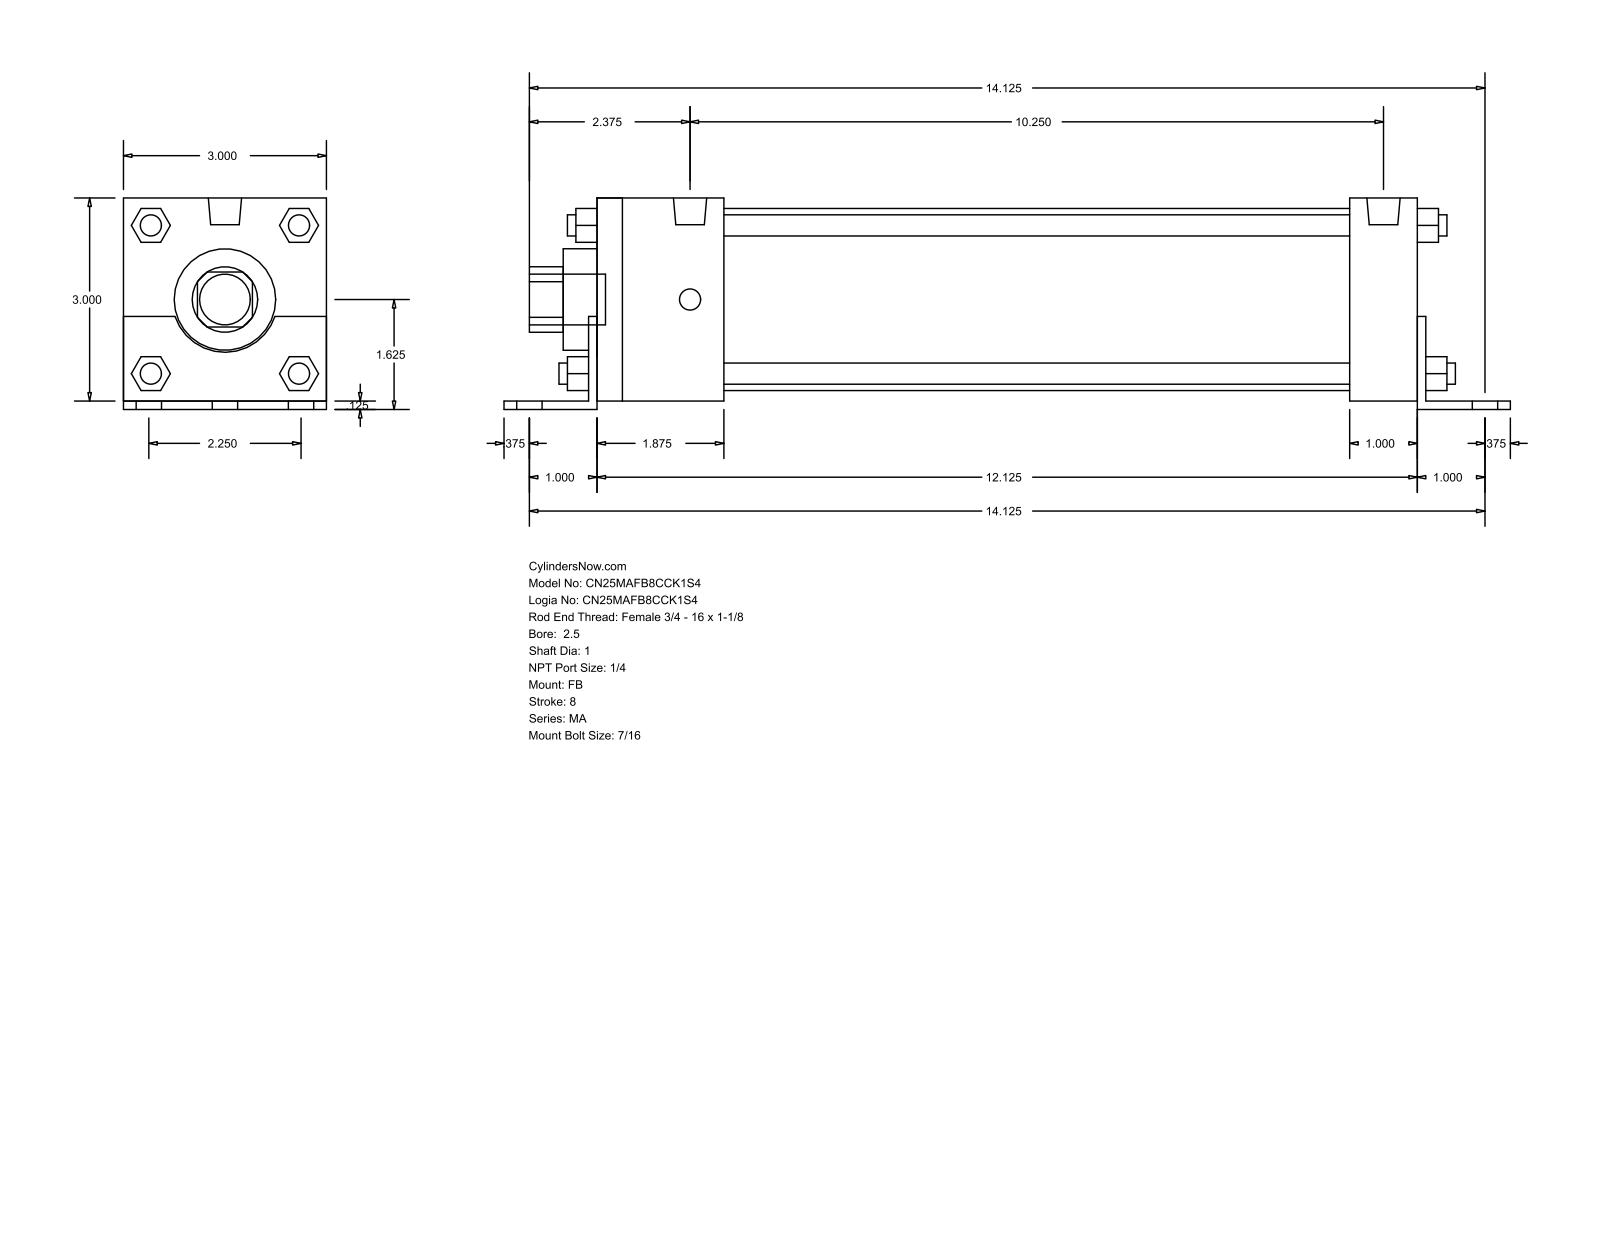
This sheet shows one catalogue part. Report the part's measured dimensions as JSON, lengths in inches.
{"part_name": "MA_FB__0250_1", "step_written_by": "GSSL Pune (CONFIG_CONTROL_DESIGN)", "units": "inches", "bodies": {"solids": 0, "faces": 140, "planar": 105, "cylindrical": 35, "other": 0}, "overall_size": [14.875, 3.125, 3], "round_holes": [[1, 1], [1.5, 1], [2.69, 1]], "round_bosses_or_shafts": [[0.313, 8], [0.437, 6], [0.492, 2], [0.75, 1]], "partial_cylinders_radius": [[0.484, 1], [0.78, 1]], "face_to_face_distances": [3, 0.125, 3.125, 12.25, 12.125, 0.5, 1, 1.125, 1.875, 10.25]}
